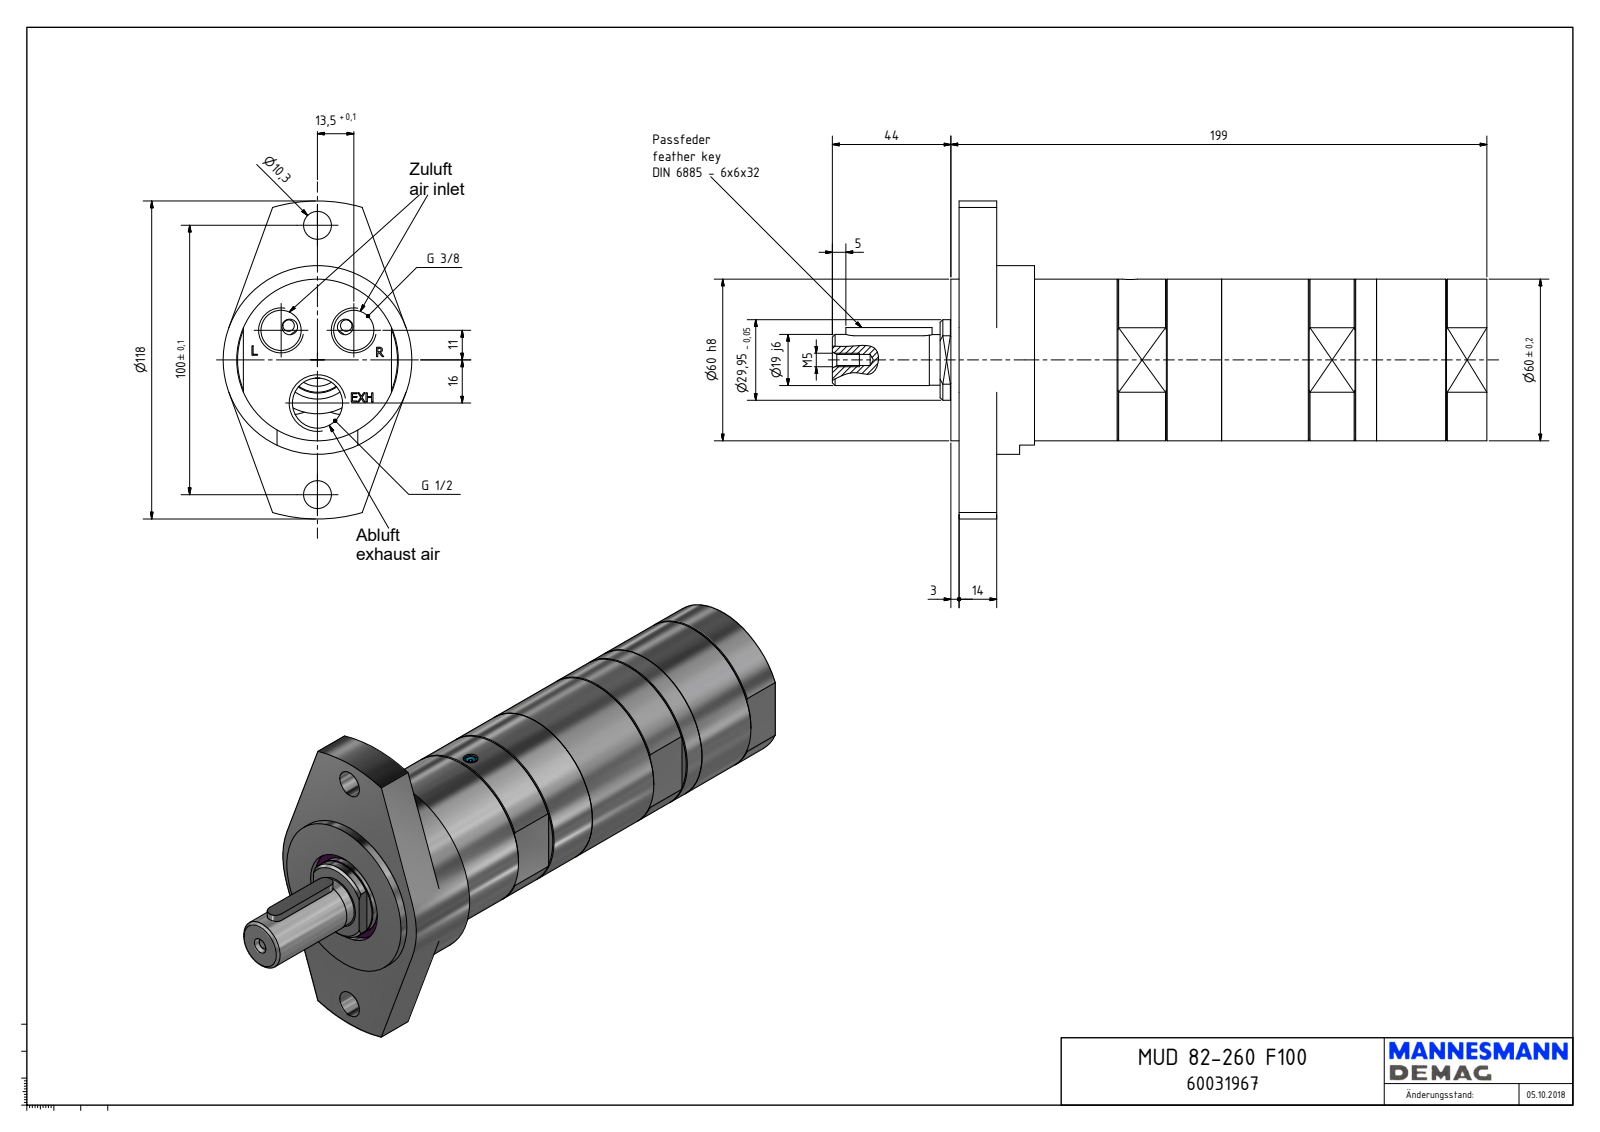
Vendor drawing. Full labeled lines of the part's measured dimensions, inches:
Part name (STEP PRODUCT): MUD 82-260 F100_60031967
STEP written by: Autodesk Inventor 2018 (AUTOMOTIVE_DESIGN)
Units: inches
Bodies: 1 solid, 203 faces (114 planar, 47 cylindrical, 42 other)
Overall size (bounding box): 9.567 × 4.646 × 2.756
Volume: 37.66 in³ · Surface area: 95.32 in²
Round holes (diameter × count): ⌀0.406 ×2, ⌀0.589 ×2, ⌀0.061 ×1, ⌀0.157 ×1, ⌀0.163 ×1, ⌀0.217 ×1, ⌀0.733 ×1, ⌀1.378 ×1, ⌀1.575 ×1
Round bosses / shafts (diameter × count): ⌀2.756 ×1, ⌀2.362 ×1, ⌀1.179 ×1, ⌀0.748 ×1, ⌀0.74 ×1, ⌀0.197 ×1, ⌀0.142 ×1
Partial cylindrical surfaces — rounded edges, fillets, slot ends (radius × count): R0.118 ×2, R0.295 ×2, R0.335 ×1, R0.746 ×1, R0.925 ×1, R1.015 ×1, R1.196 ×1, R2.323 ×1
Main face-to-face distances: 0.551, 0.669, 0.118, 7.717, 7.165, 7.835, 2.165, 1.22, 1.102, 6.614
Hole centre spacings: 0.685, 1.189, 1.625, 1.969, 2.46, 0.63, 1.063, 1.339
